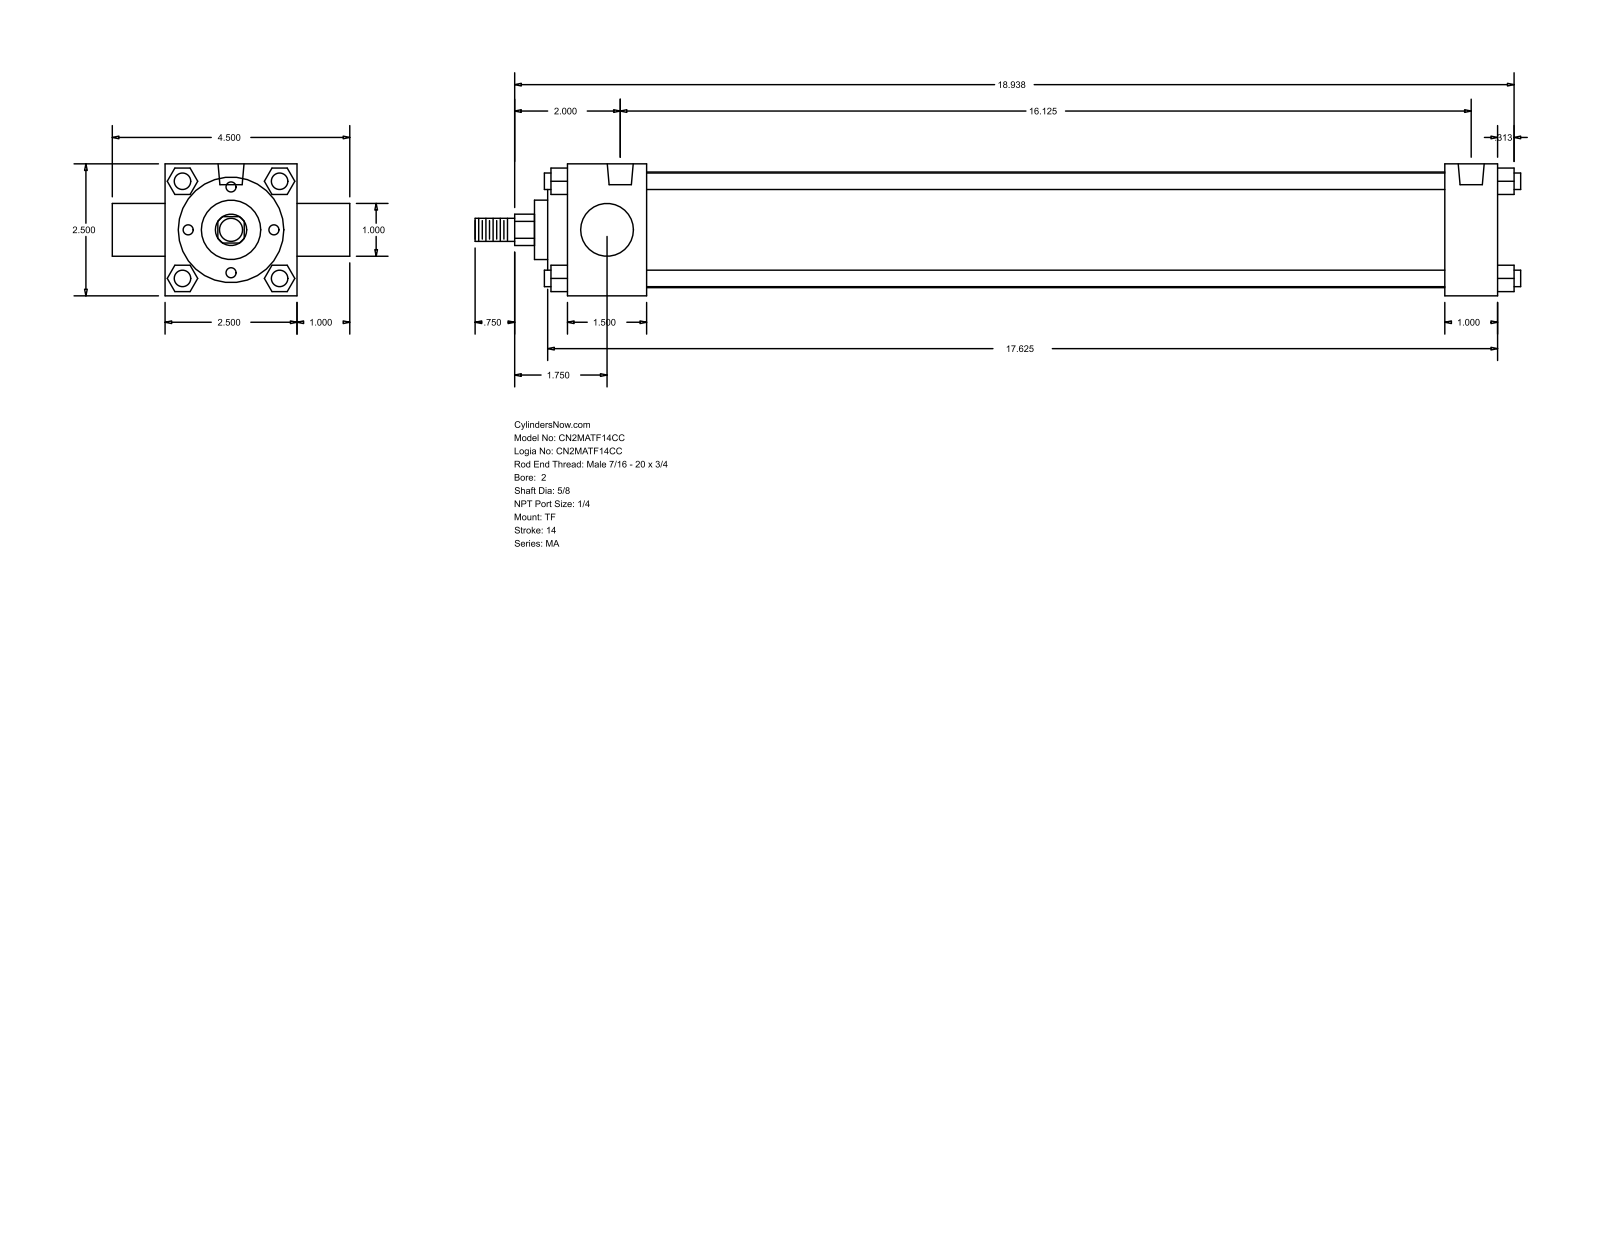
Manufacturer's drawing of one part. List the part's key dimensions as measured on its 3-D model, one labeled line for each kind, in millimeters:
Part name (STEP PRODUCT): MA_TF__0200_0.625
STEP written by: GSSL Pune (CONFIG_CONTROL_DESIGN)
Units: millimetres
Bodies: 0 solids, 122 faces (93 planar, 29 cylindrical, 0 other)
Overall size (bounding box): 503.24 × 114.3 × 63.5
Round holes (diameter × count): ⌀7.94 ×3, ⌀12.49 ×2
Round bosses / shafts (diameter × count): ⌀7.94 ×4, ⌀55.63 ×1, ⌀50.8 ×1, ⌀28.57 ×1, ⌀25.4 ×1, ⌀15.88 ×1, ⌀11.11 ×1
Partial cylindrical surfaces — rounded edges, fillets, slot ends (radius × count): R7.54 ×1
Main face-to-face distances: 63.5, 38.1, 12.7, 447.67, 422.28, 384.18, 409.57, 25.39, 9.52, 47.62
Hole centre spacings: 409.58
